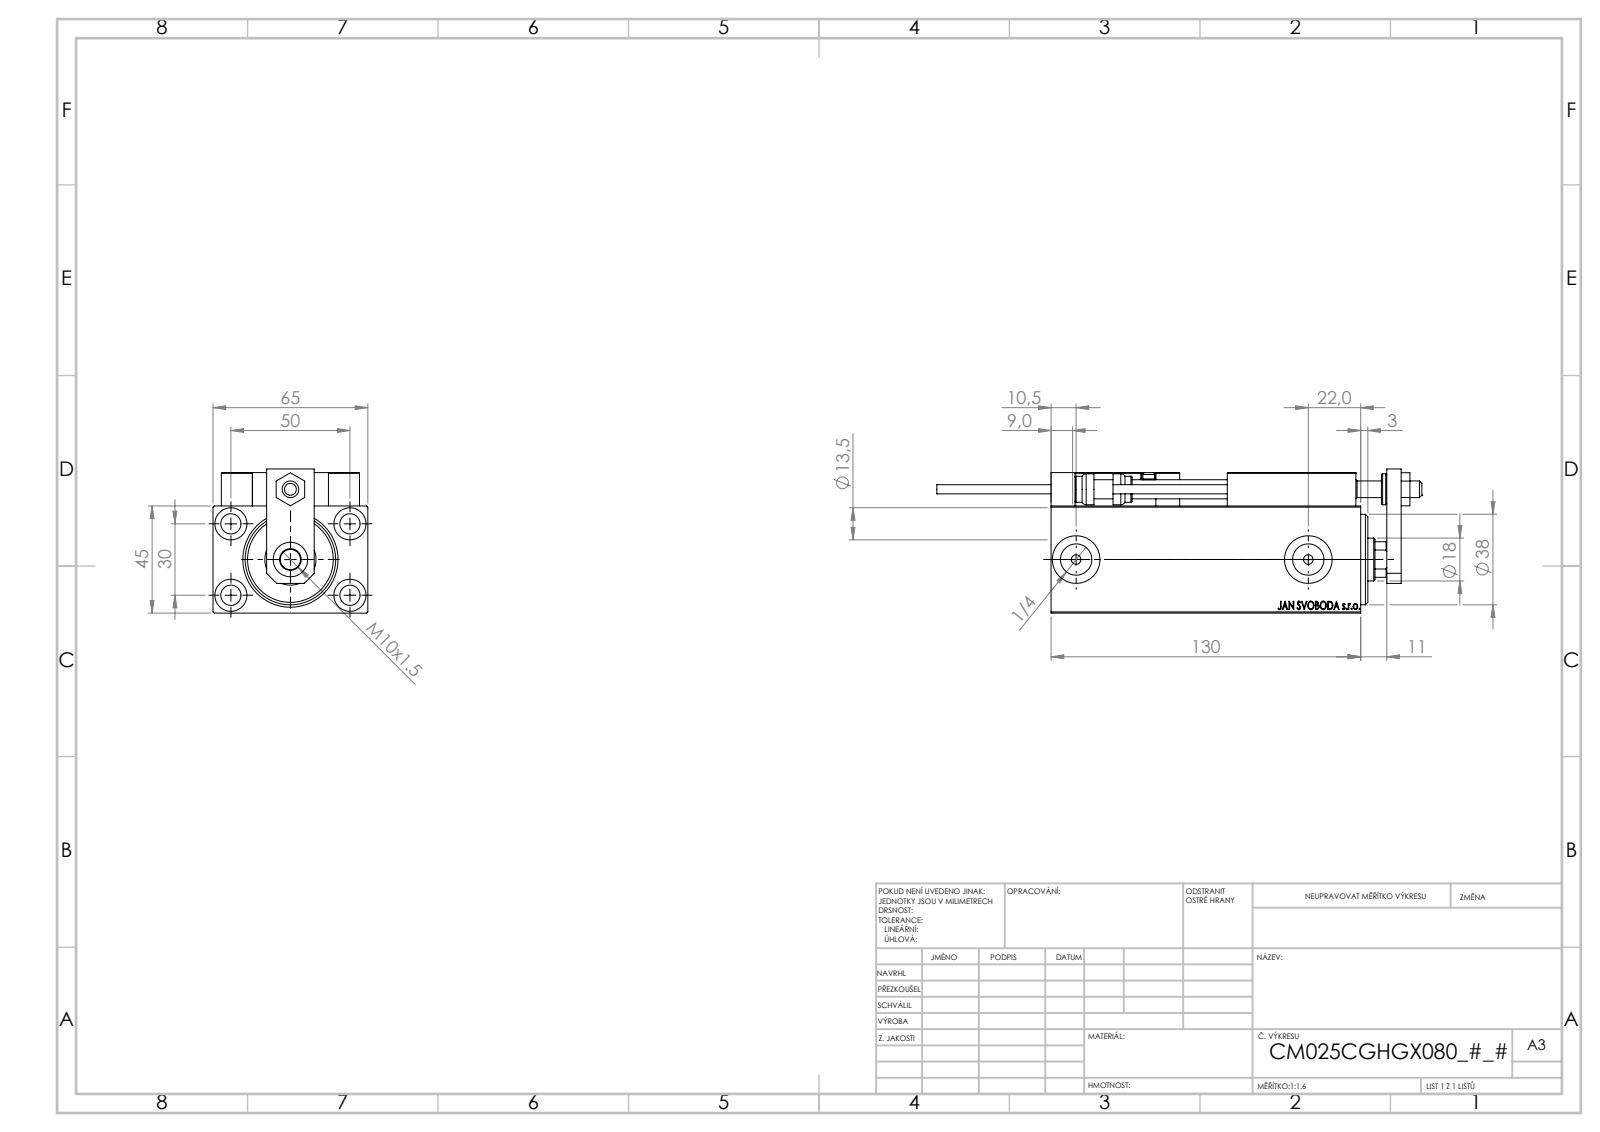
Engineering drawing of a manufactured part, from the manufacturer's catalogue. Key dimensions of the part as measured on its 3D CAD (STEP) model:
Part name (STEP PRODUCT): Block; ZARAZKA; V450CM_C_Body; SWITCH DIM B,W (+7 more)
STEP written by: SolidWorks 2019 (CONFIG_CONTROL_DESIGN)
Units: millimetres
Bodies: 23 solids, 1282 faces (560 planar, 188 cylindrical, 534 other)
Overall size (bounding box): 203.7 × 65 × 60.5
Volume: 373 805 mm³ · Surface area: 99 913 mm²
Round holes (diameter × count): ⌀4 ×6, ⌀8 ×5, ⌀8.5 ×5, ⌀3.2 ×4, ⌀13.5 ×4, ⌀5 ×2, ⌀13.16 ×2, ⌀20 ×2, ⌀7 ×1, ⌀14.5 ×1, ⌀18 ×1, ⌀21.5 ×1
Round bosses / shafts (diameter × count): ⌀5 ×2, ⌀3.8 ×2, ⌀13 ×1, ⌀11 ×1
Partial cylindrical surfaces — rounded edges, fillets, slot ends (radius × count): R0.3 ×30, R3 ×2, R8.5 ×1
Main face-to-face distances: 45, 65, 14, 6, 59, 3, 13, 3.5, 7, 20
Hole centre spacings: 29.15, 11.37, 20, 28.9, 29.59, 29.69, 30, 36.06
